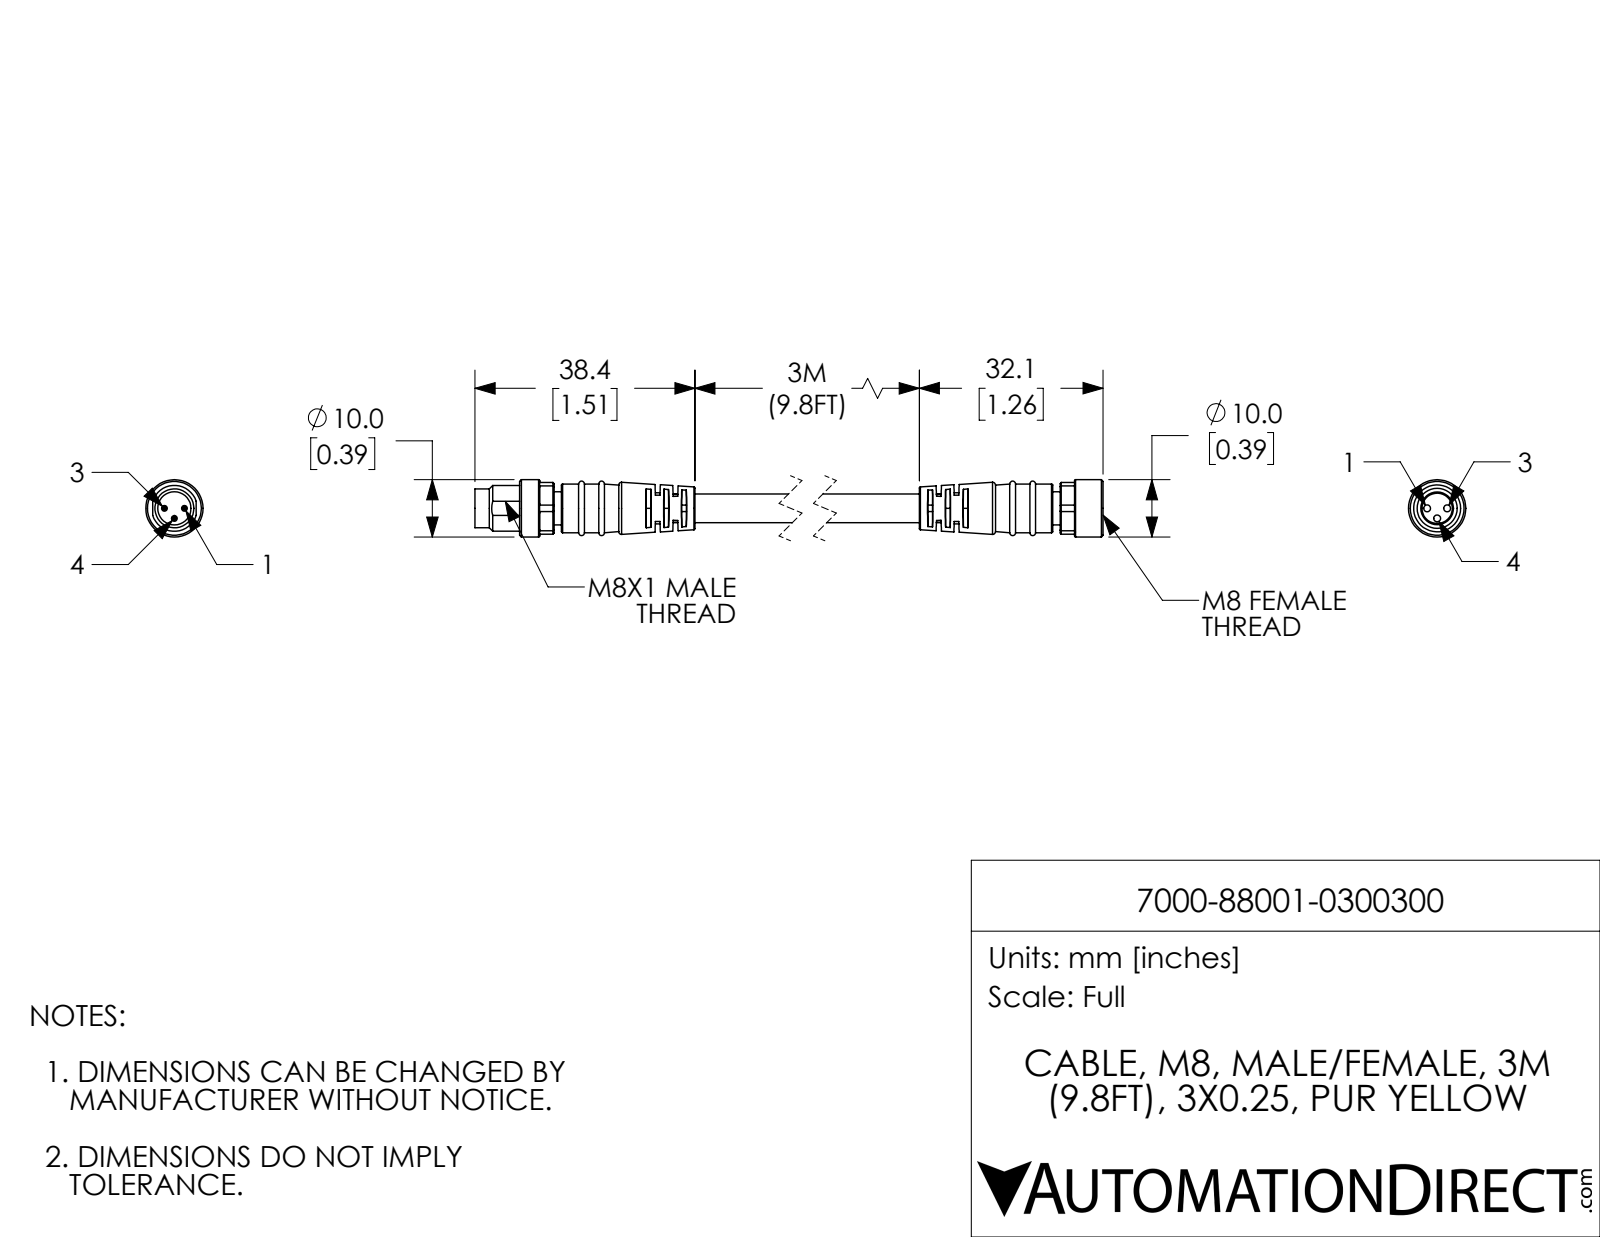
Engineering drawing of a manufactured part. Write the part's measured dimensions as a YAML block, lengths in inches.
part_name: "7000-88001-0300300; 7000-88001-0300300_MALE; 7000-88001-0300300_FEMALE"
step_written_by: "SolidWorks 2021 (CONFIG_CONTROL_DESIGN)"
units: inches
bodies: {solids: 2, faces: 273, planar: 138, cylindrical: 66, other: 69}
overall_size: [4.823, 0.394, 0.394]
volume: 0.272
surface_area: 5.608
round_holes:
  - {diameter: 0.047, count: 3}
  - {diameter: 0.276, count: 1}
round_bosses_or_shafts:
  - {diameter: 0.039, count: 3}
  - {diameter: 0.394, count: 1}
  - {diameter: 0.335, count: 1}
  - {diameter: 0.315, count: 1}
  - {diameter: 0.268, count: 1}
  - {diameter: 0.228, count: 1}
  - {diameter: 0.224, count: 1}
  - {diameter: 0.197, count: 1}
partial_cylinders:
  - {radius: 0.193, count: 1}
face_to_face_distances: [0.122, 0.122, 0.025, 4.28, 0.147, 0.354, 0.051, 3.933, 0.026, 0.346]
hole_center_spacings: [0.069, 0.097, 0.138]
